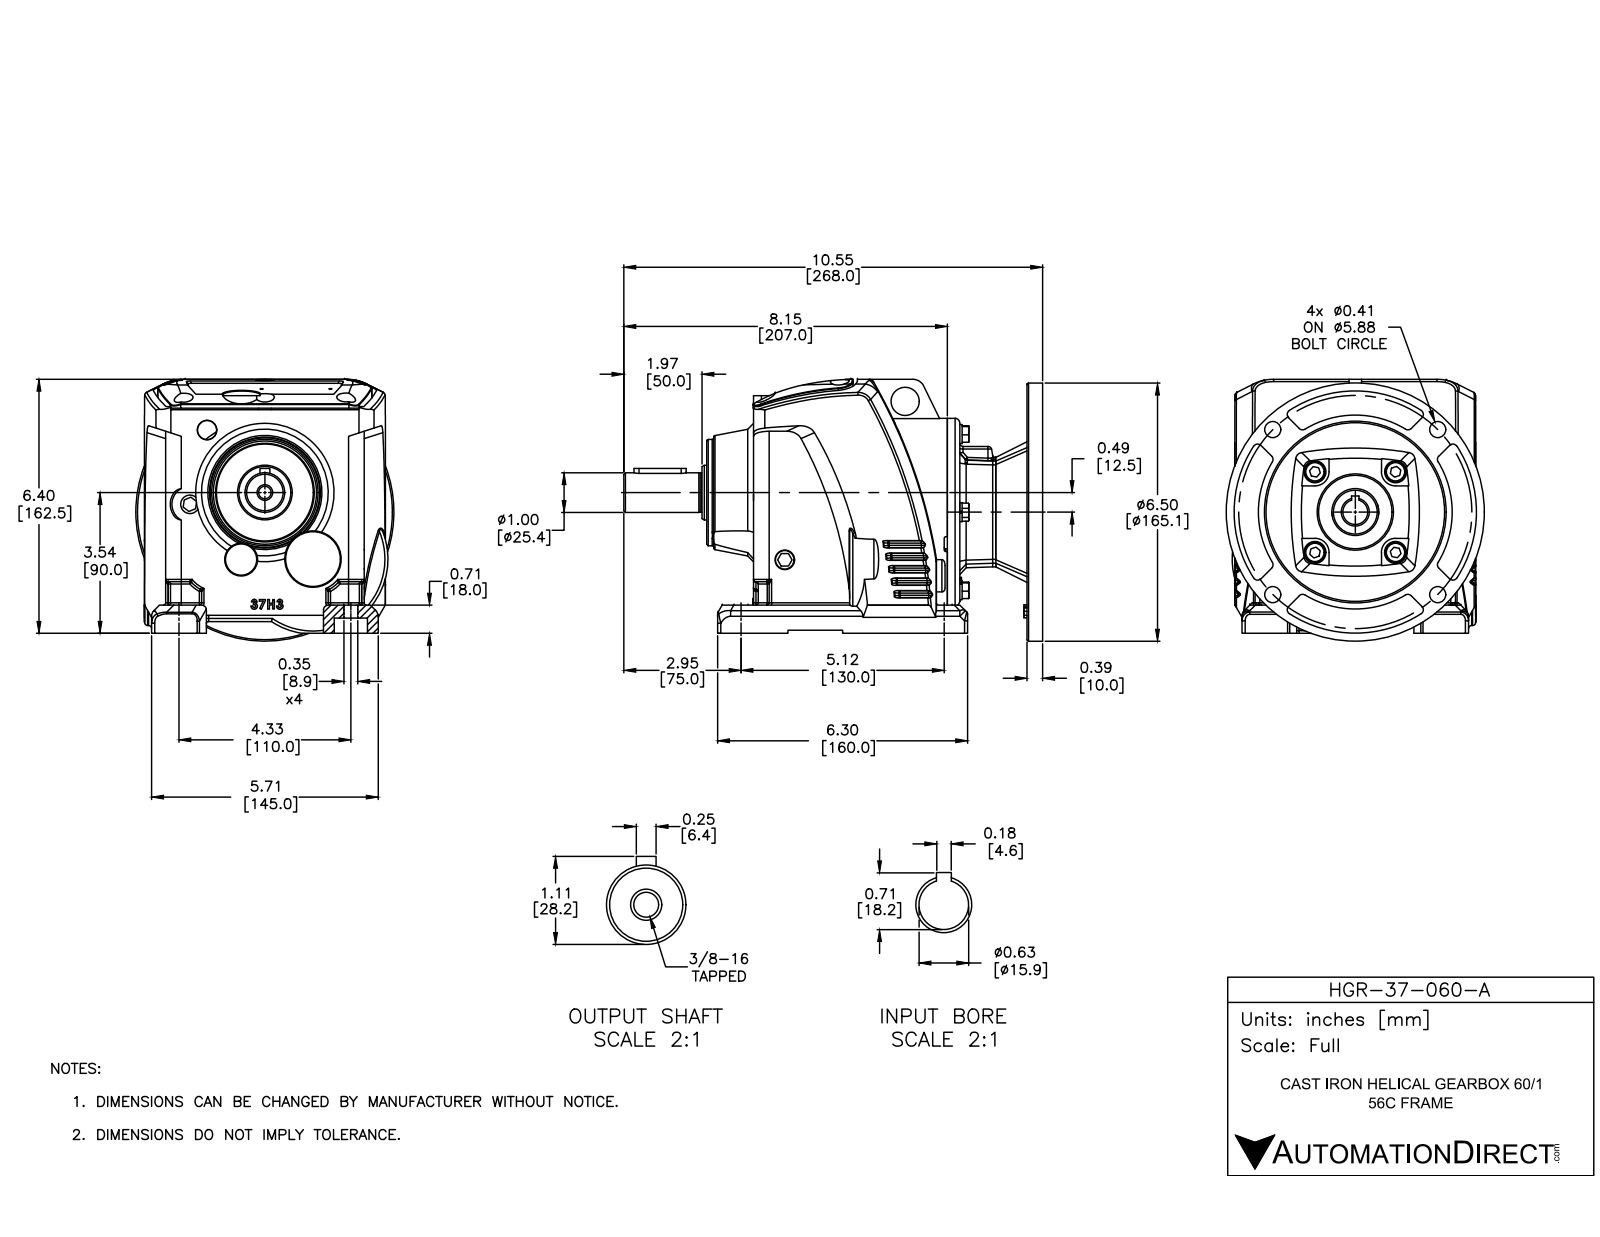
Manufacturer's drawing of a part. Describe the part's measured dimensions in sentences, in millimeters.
The part is named "HGR-37-060-A". Its 3-D file was written by "SolidWorks 2015 (AUTOMOTIVE_DESIGN)". It is 4 solids with 1036 faces: 343 planar, 277 cylindrical and 416 other. Overall it measures 268 by 167.5 by 165.1 millimeters. Its volume is 2 781 000 cubic millimeters and its surface area 247 600 square millimeters. Round holes: 6 of diameter 12, 4 of diameter 10.3, 4 of diameter 14, 3 of diameter 7, 2 of diameter 2, 2 of diameter 9, 2 of diameter 10, 1 of diameter 8, 1 of diameter 15.9, 1 of diameter 18, 1 of diameter 24, 1 of diameter 30. Round bosses or shafts: 4 of diameter 13, 4 of diameter 12.2, 4 of diameter 8, 2 of diameter 35, 2 of diameter 12, 1 of diameter 165.1, 1 of diameter 120, 1 of diameter 68. Partial cylindrical surfaces (rounded edges, fillets, slot ends): 43 of radius 1.5, 21 of radius 3, 18 of radius 2, 8 of radius 5, 6 of radius 9, 6 of radius 10, 5 of radius 8, 4 of radius 7. The main face-to-face distances are 181, 6, 7, 10, 175, 28, 110, 4, 53, 2. The hole center spacings are 83.1, 36.5, 38.1, 51.6, 74.6, 105.5, 111.1, 29.
